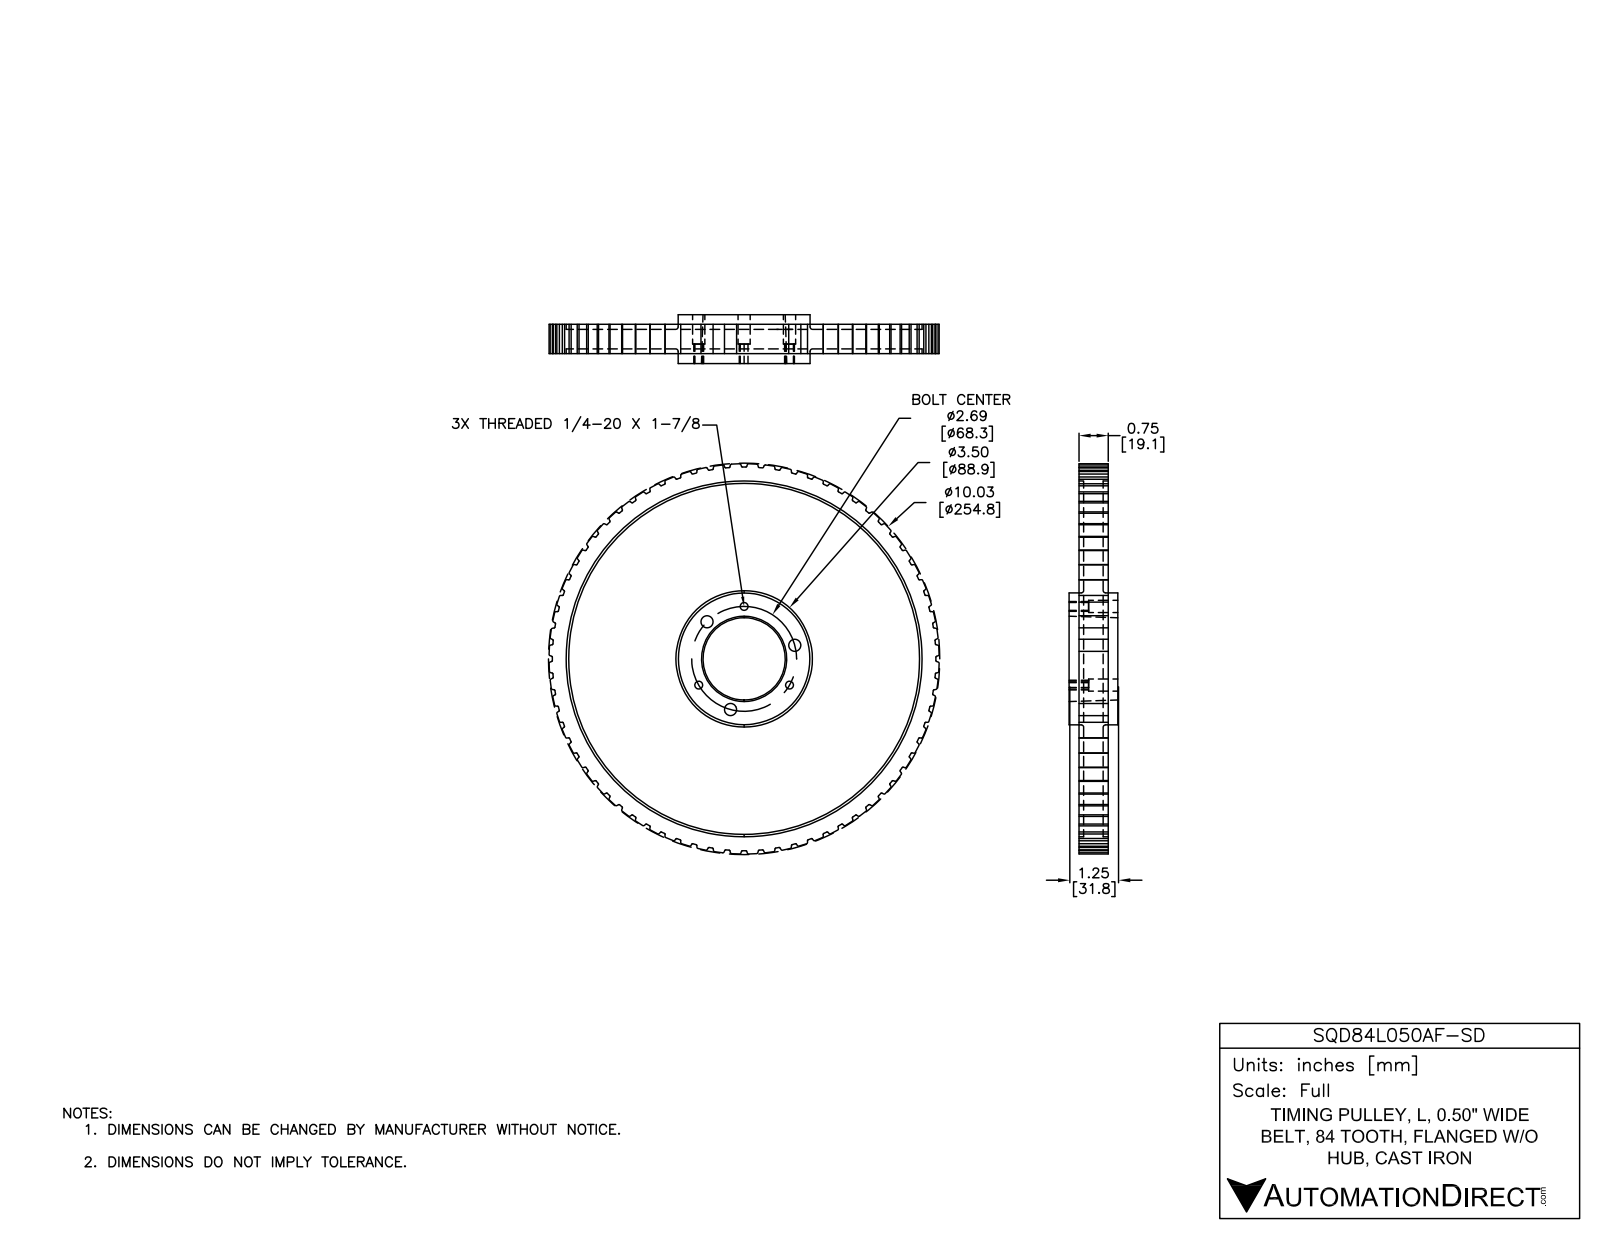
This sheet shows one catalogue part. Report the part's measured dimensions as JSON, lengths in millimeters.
{"part_name": "SQD84L050AF-SD", "step_written_by": "SolidWorks 2014 (AUTOMOTIVE_DESIGN)", "units": "millimeters", "bodies": {"solids": 1, "faces": 675, "planar": 225, "cylindrical": 440, "other": 10}, "overall_size": [253.9, 253.9, 31.8], "volume_mm3": 715300, "surface_area_mm2": 131900, "round_holes": [[5.1, 3], [7.9, 3], [8, 3], [231.6, 1]], "round_bosses_or_shafts": [[85.9, 1]], "partial_cylinders_radius": [[0.5, 144], [0.8, 144], [127, 1]], "face_to_face_distances": [12.7, 19.1, 3.2, 15.9, 15.9, 3.2, 6.5, 9.4, 9.7, 22.4], "hole_center_spacings": [34.1, 59.1, 59.1, 67.7, 26.1, 41.6, 26.1, 34.1]}
